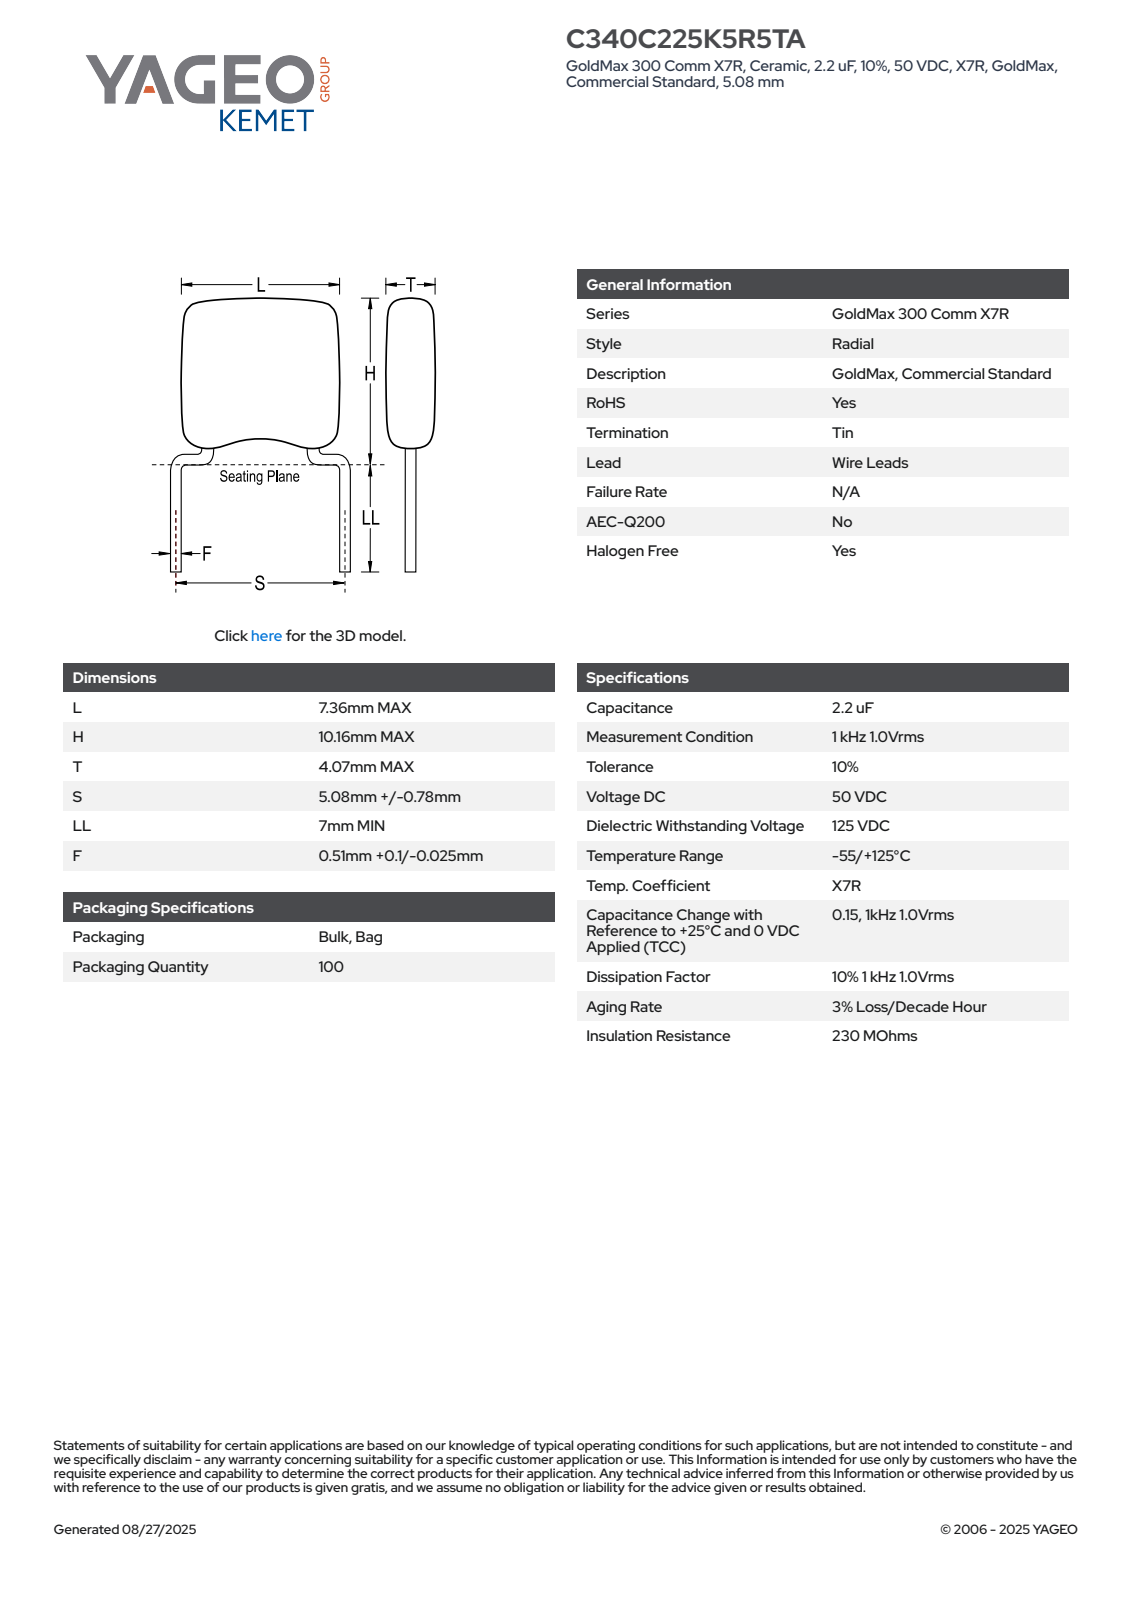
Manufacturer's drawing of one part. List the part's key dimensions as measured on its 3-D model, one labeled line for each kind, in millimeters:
Part name (STEP PRODUCT): CCR_SB_7.36X10.16_L7.36H10.16T4.07S5.08LL7F0.51
STEP written by: SolidWorks 2014 (AUTOMOTIVE_DESIGN)
Units: millimetres
Bodies: 4 solids, 97 faces (65 planar, 14 cylindrical, 18 other)
Overall size (bounding box): 17.16 × 7.36 × 4.08
Volume: 200 mm³ · Surface area: 227 mm²
Round bosses / shafts (diameter × count): ⌀0.51 ×2
Partial cylindrical surfaces — rounded edges, fillets, slot ends (radius × count): R1 ×10
Main face-to-face distances: 4.07, 7.36, 6.97, 4.08, 3.82, 3.15, 3.2, 0.62, 3.77, 0.56
